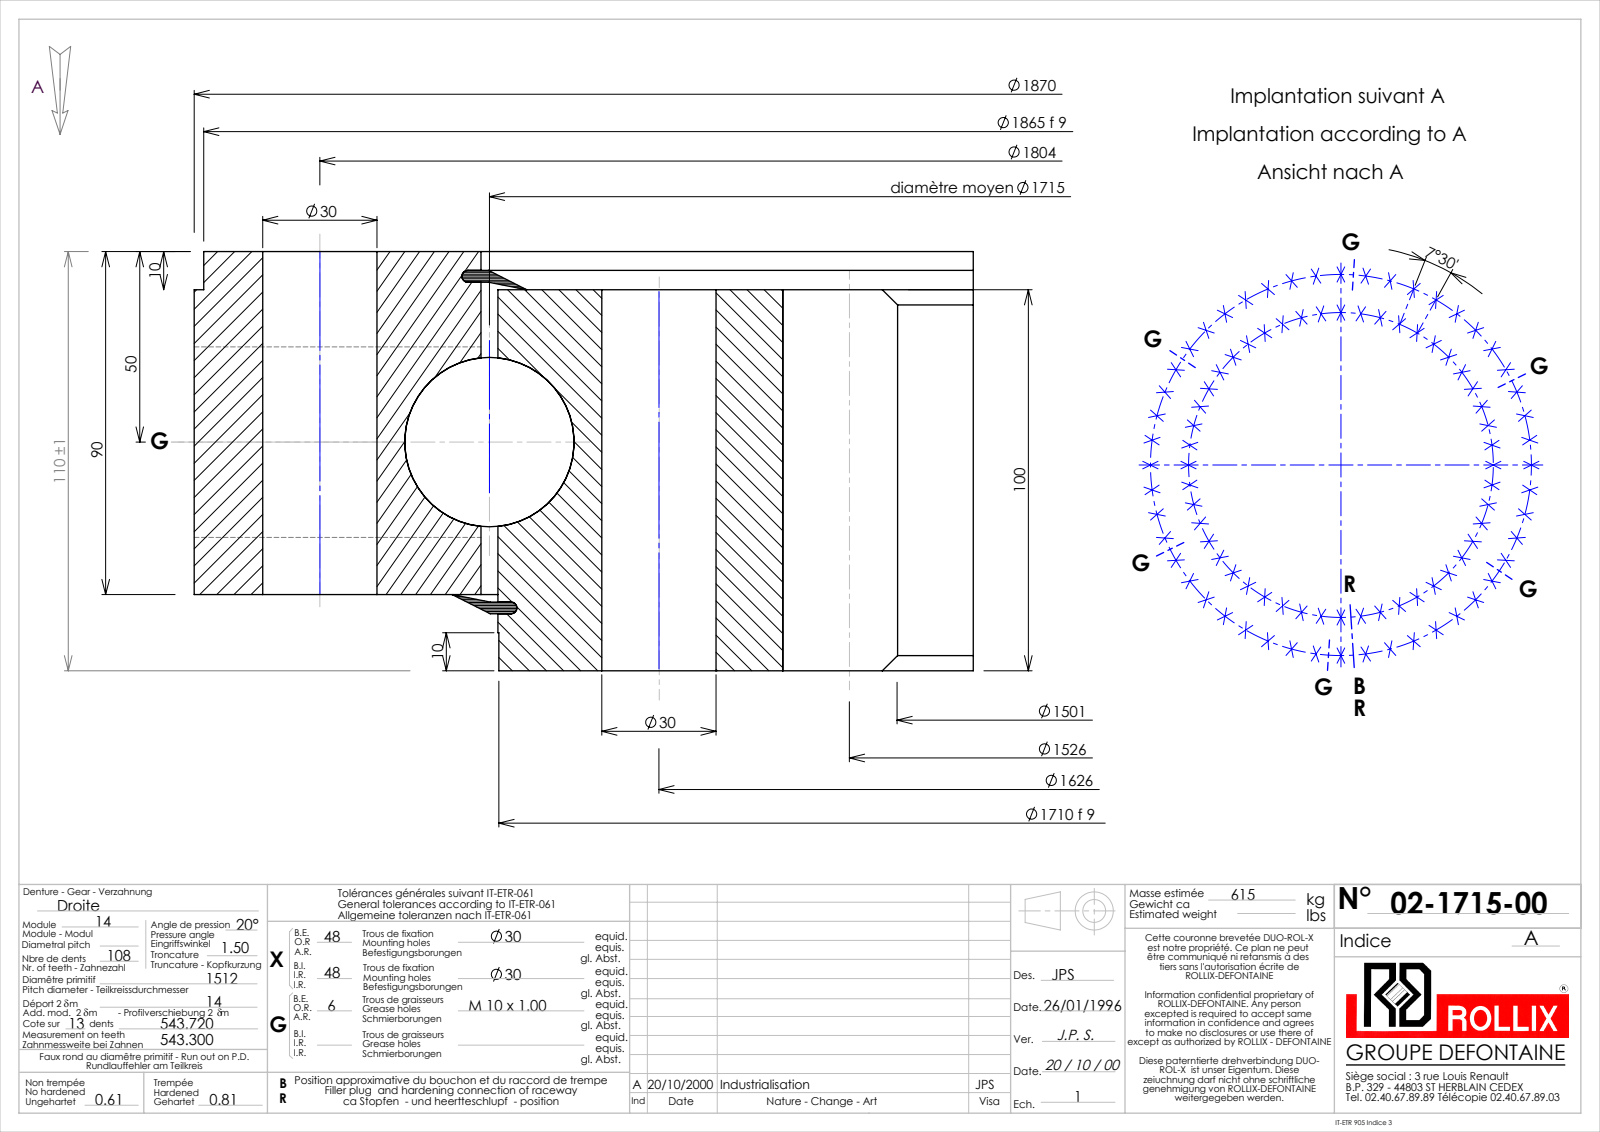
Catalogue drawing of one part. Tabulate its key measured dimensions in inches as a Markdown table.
| quantity | value |
| --- | --- |
| part name | 02-1715-00 |
| STEP written by | SolidWorks 2016 (CONFIG_CONTROL_DESIGN) |
| units | inches |
| bodies | 5 solids, 913 faces (230 planar, 439 cylindrical, 244 other) |
| overall size | 73.622 × 73.622 × 4.331 |
| volume | 4 320 in³ |
| surface area | 8 843 in² |
| round holes (diameter × count) | 1.181 × 96, 0.354 × 6, 67.694 × 1 |
| round bosses / shafts (diameter × count) | 73.622 × 1, 73.425 × 1, 67.345 × 1, 67.323 × 1 |
| partial cylindrical surfaces (radius × count) | 29.547 × 1, 30.728 × 1 |
| main face-to-face distances | 3.937, 0.787, 3.15, 0.394, 3.543, 4.331, 0.199, 3.348, 0.077, 3.226 |
| hole center spacings | 16.569, 20.577, 24.498, 28.313, 12.489, 8.356, 4.187, 32.008 |
